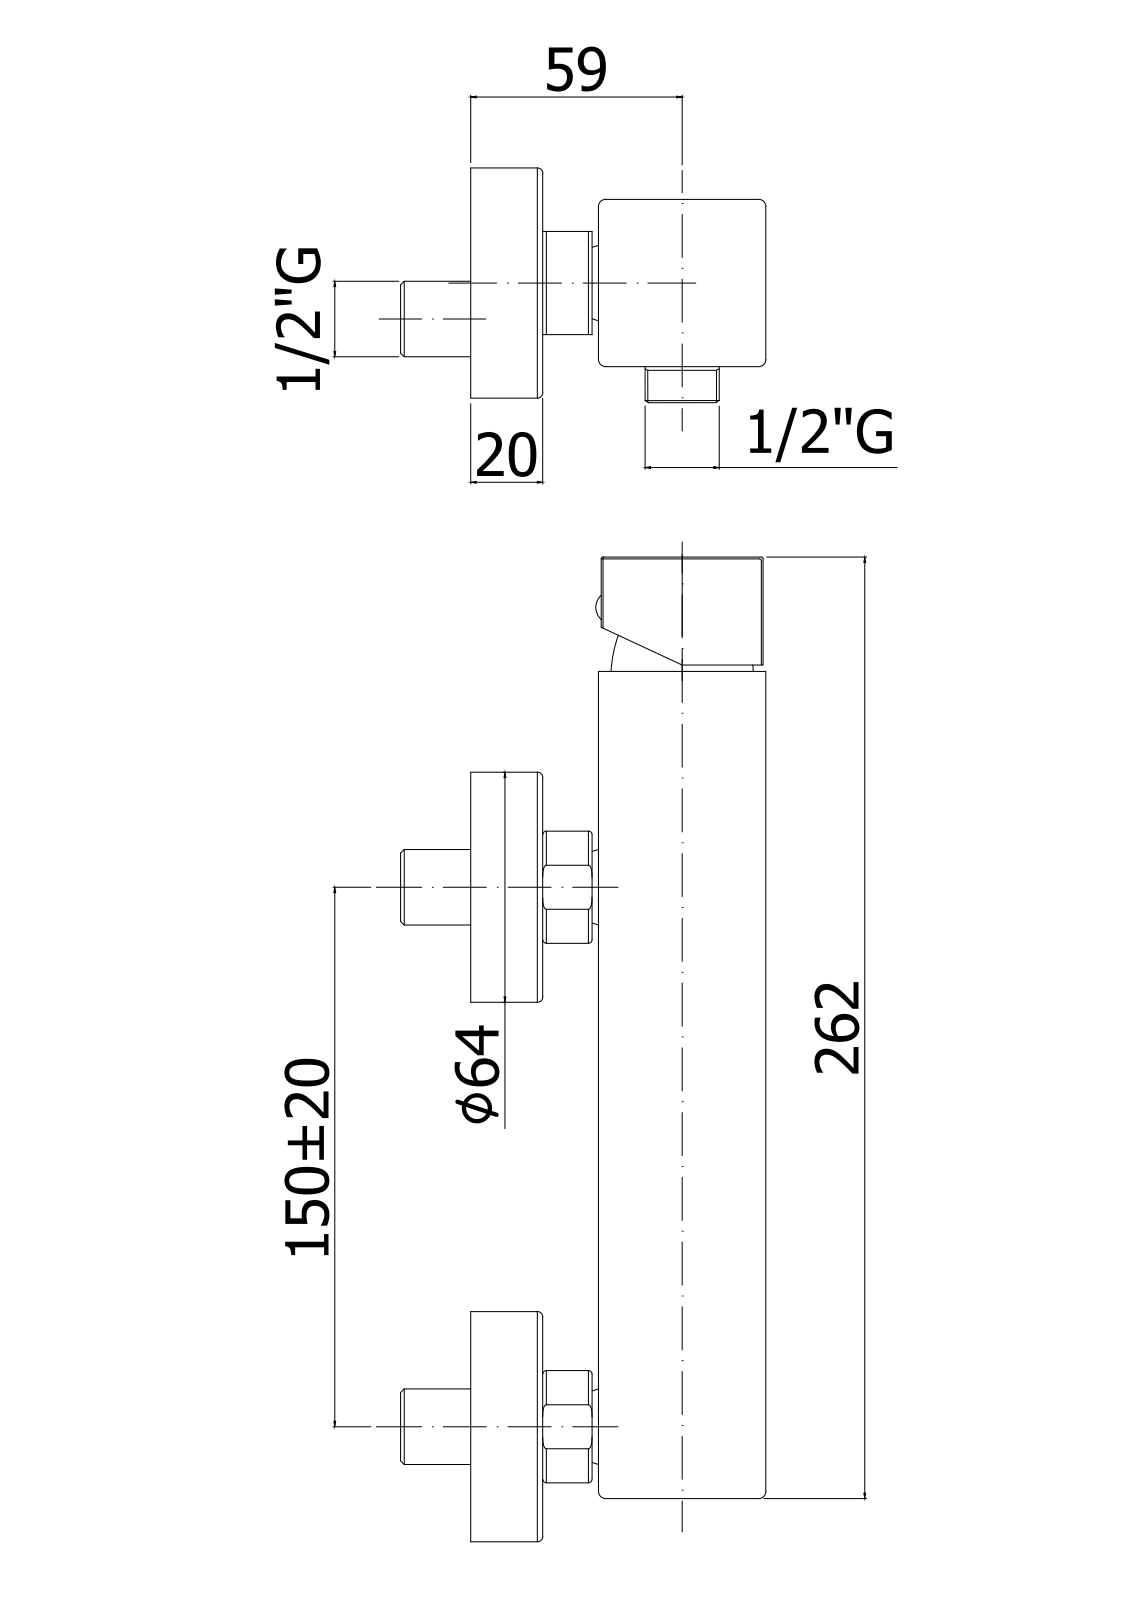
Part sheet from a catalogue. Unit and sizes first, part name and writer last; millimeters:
Units: millimetres
Overall size (bounding box): 272.75 × 81.5 × 65.5
Round holes (diameter × count): ⌀42 ×1
Round bosses / shafts (diameter × count): ⌀63.5 ×2, ⌀20.9 ×1, ⌀18 ×1, ⌀15 ×1, ⌀9 ×1, ⌀8 ×1, ⌀5 ×1
Partial cylindrical surfaces — rounded edges, fillets, slot ends (radius × count): R1 ×8, R1.5 ×4, R15.6 ×2, R3 ×1, R3.95 ×1
Main face-to-face distances: 46.5, 35, 81.5, 15, 20, 61.5, 0.75, 45.75, 45, 261
Volume: 686 205 mm³ · Surface area: 82 799 mm²
Bodies: 1 solid, 104 faces (33 planar, 38 cylindrical, 33 other)
Part name (STEP PRODUCT): EL168CR
STEP written by: CREO PARAMETRIC BY PTC INC, 2020044 (CONFIG_CONTROL_DESIGN)
